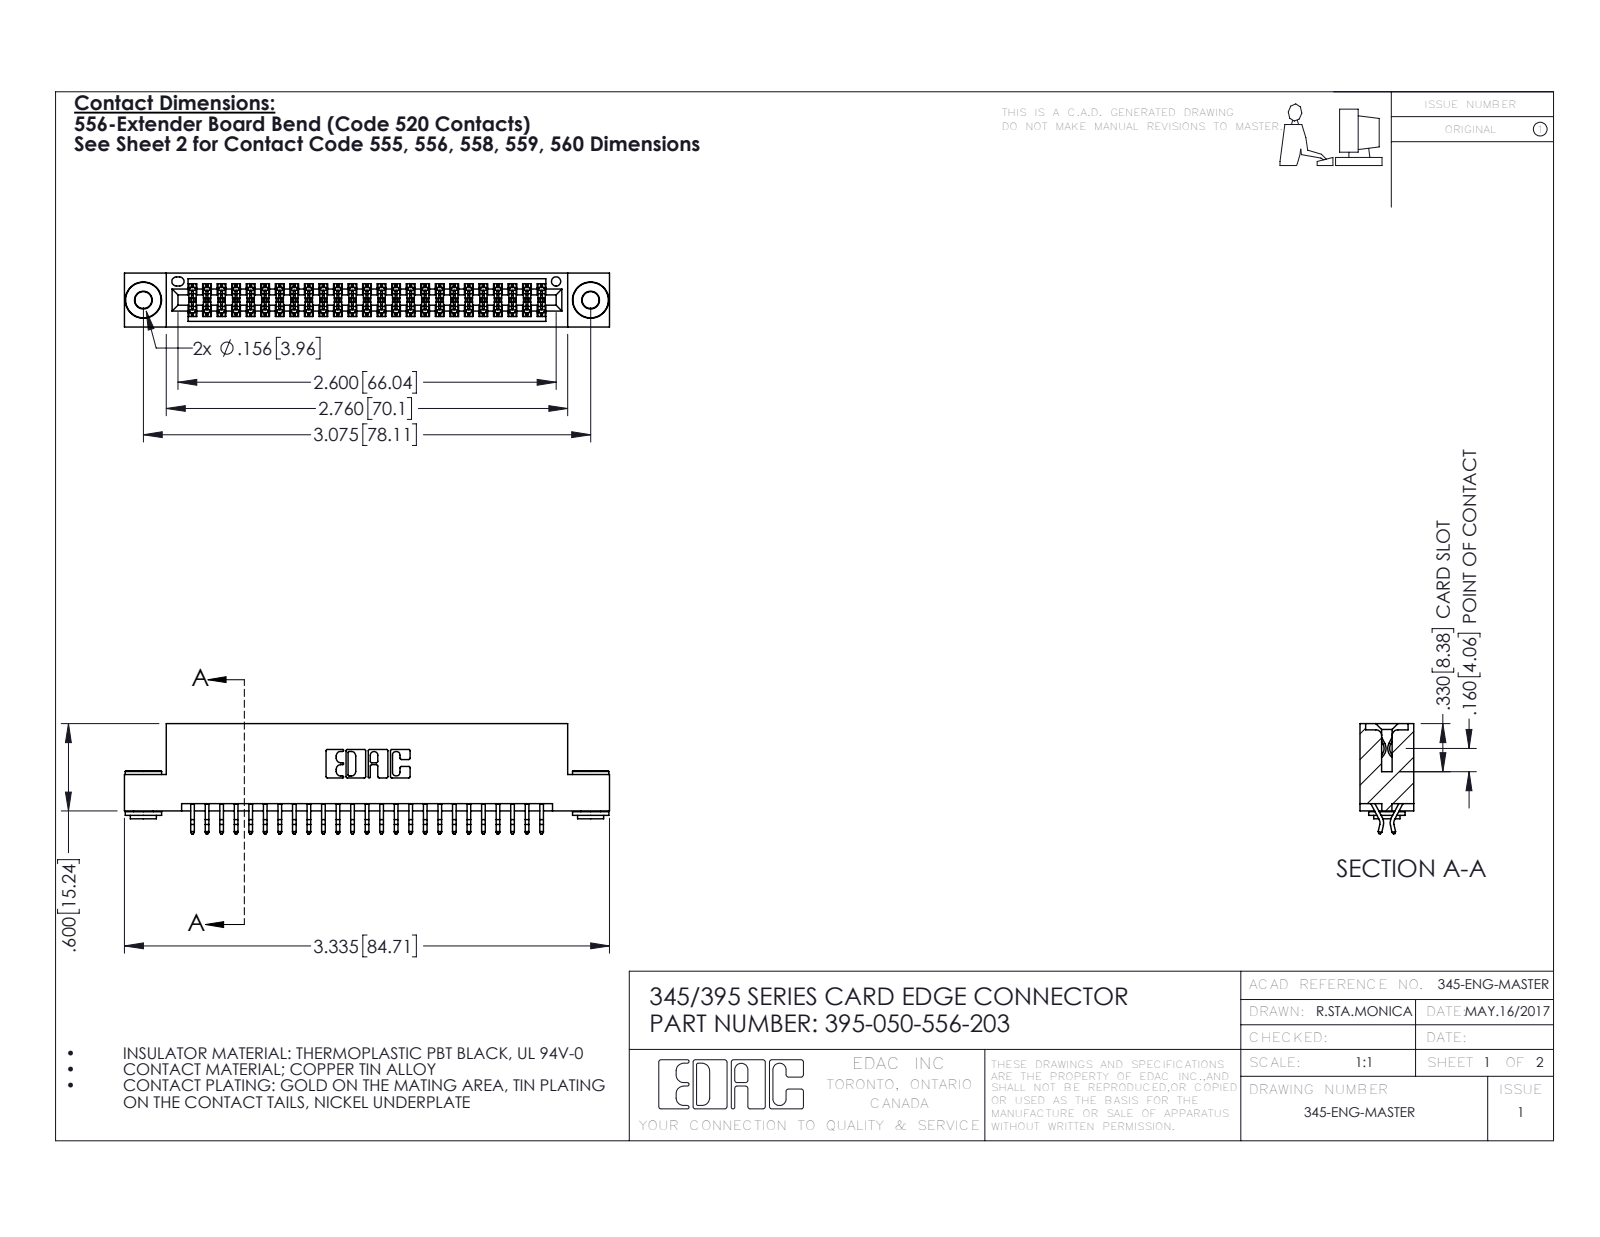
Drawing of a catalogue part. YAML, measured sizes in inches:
part_name: "395-050-556-203; 345-292-001_556 Tail; 345-250-002_345-250-002-102; 345 Part_Flush Mounting Lugs - 0.156 Dia-TH"
step_written_by: "SolidWorks 2016 (CONFIG_CONTROL_DESIGN)"
units: inches
bodies: {solids: 53, faces: 2964, planar: 1940, cylindrical: 1016, other: 8}
overall_size: [3.335, 0.757, 0.37]
volume: 0.494
surface_area: 18.27
round_holes:
  - {diameter: 0.116, count: 2}
  - {diameter: 0.156, count: 2}
  - {diameter: 0.064, count: 1}
round_bosses_or_shafts:
  - {diameter: 0.25, count: 2}
  - {diameter: 0.18, count: 2}
  - {diameter: 0.136, count: 2}
partial_cylinders:
  - {radius: 0.006, count: 75}
  - {radius: 0.01, count: 22}
  - {radius: 0.007, count: 6}
  - {radius: 0.031, count: 6}
  - {radius: 0.026, count: 3}
  - {radius: 0.01, count: 2}
  - {radius: 0.014, count: 2}
  - {radius: 0.019, count: 2}
face_to_face_distances: [0.072, 0.298, 0.2, 0.37, 0.025, 0.098, 0.272, 0.225, 0.175, 0.149]
hole_center_spacings: [0.27, 2.84, 3.075]
